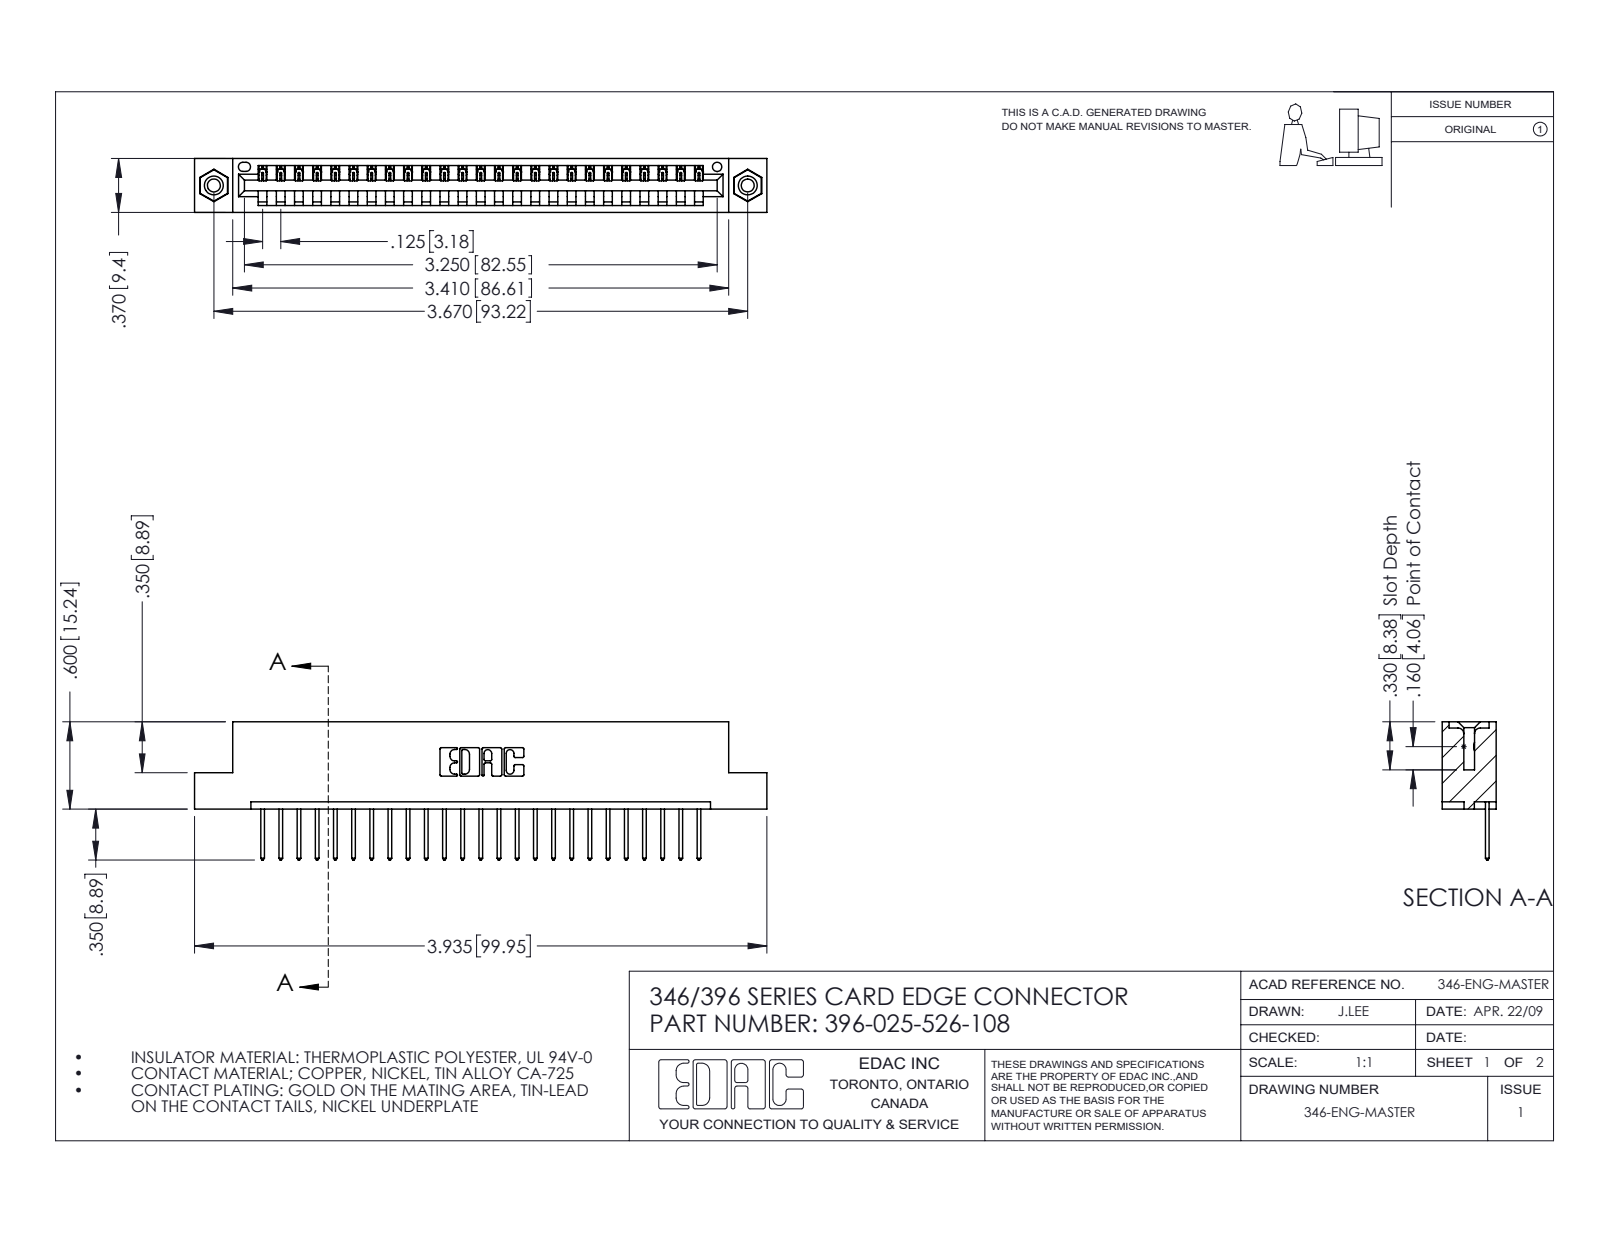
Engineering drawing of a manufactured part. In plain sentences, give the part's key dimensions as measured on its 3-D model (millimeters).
The part is named "345-250-001_345-250-003-102; 396-025-526-108; 345-292-001_345-293-126; 346 Part_Flush Mounting Lugs - 0.156 Dia-TI". Its 3-D file was written by "SolidWorks 2016 (CONFIG_CONTROL_DESIGN)". It is 28 solids with 1632 faces: 1108 planar, 508 cylindrical and 16 other. Overall it measures 99.9 by 24.1 by 9.4 millimeters. Its volume is 9 420 cubic millimeters and its surface area 11 590 square millimeters. Round holes: 2 of diameter 2.3, 2 of diameter 3.2, 2 of diameter 4, 1 of diameter 1.6. Round bosses or shafts: 2 of diameter 3.9. Partial cylindrical surfaces (rounded edges, fillets, slot ends): 50 of radius 0.2, 50 of radius 0.3, 22 of radius 0.3, 6 of radius 0.2, 6 of radius 0.8, 3 of radius 0.7, 2 of radius 0.8, 2 of radius 1. The main face-to-face distances are 1.2, 8.2, 9.4, 6.4, 1.8, 7.6, 0.6, 3.8, 5.6, 2.5. The hole center spacings are 6.2, 87.9, 93.2.
